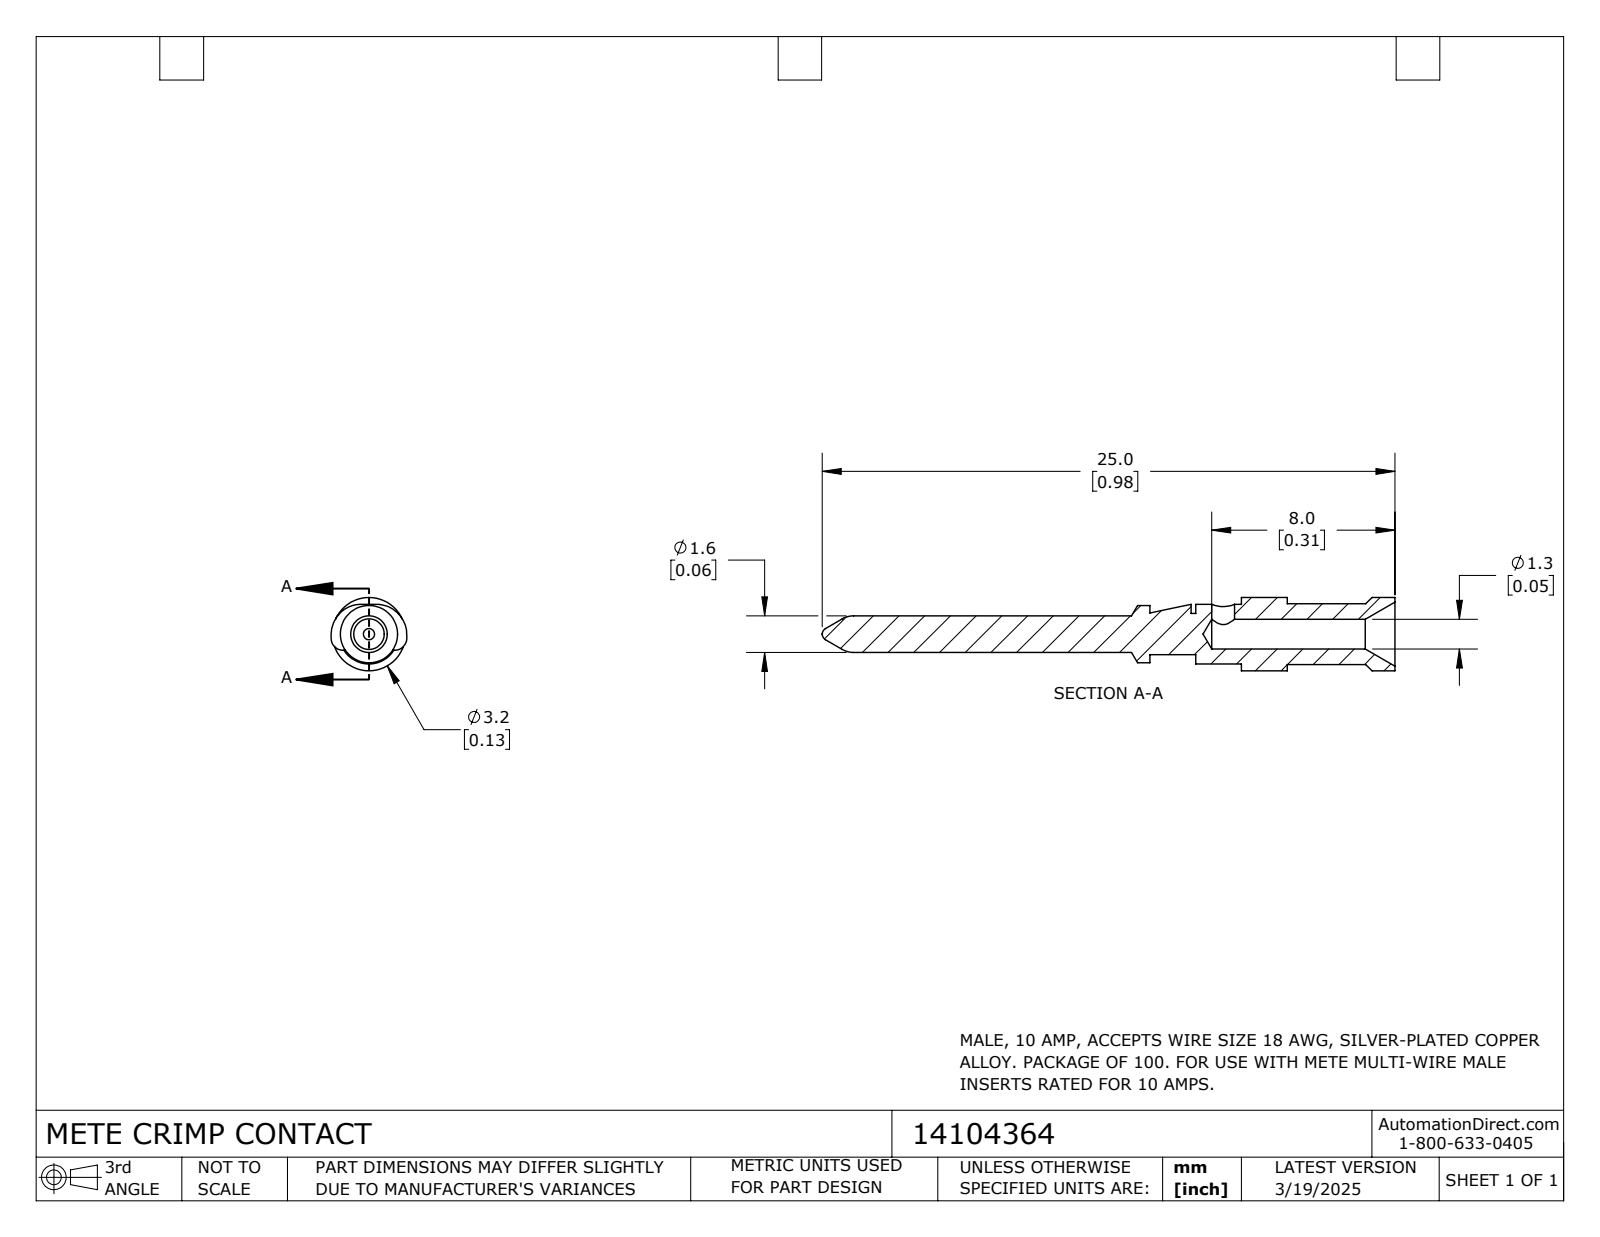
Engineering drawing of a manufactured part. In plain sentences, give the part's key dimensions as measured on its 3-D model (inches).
The part is named "14104364". Its 3-D file was written by "SolidWorks 2024 (CONFIG_CONTROL_DESIGN)". It is 1 solid with 40 faces: 7 planar, 18 cylindrical and 15 other. Overall it measures 0.984 by 0.13 by 0.126 inches. Its volume is 0.005 cubic inches and its surface area 0.344 square inches. Round holes: 1 of diameter 0.039, 1 of diameter 0.051. Round bosses or shafts: 1 of diameter 0.126, 1 of diameter 0.104, 1 of diameter 0.102, 1 of diameter 0.098, 1 of diameter 0.071, 1 of diameter 0.063. The main face-to-face distances are 0.079, 0.157, 0.087, 0.165, 0.236, 0.071, 0.185, 0.264, 0.343, 0.35.
